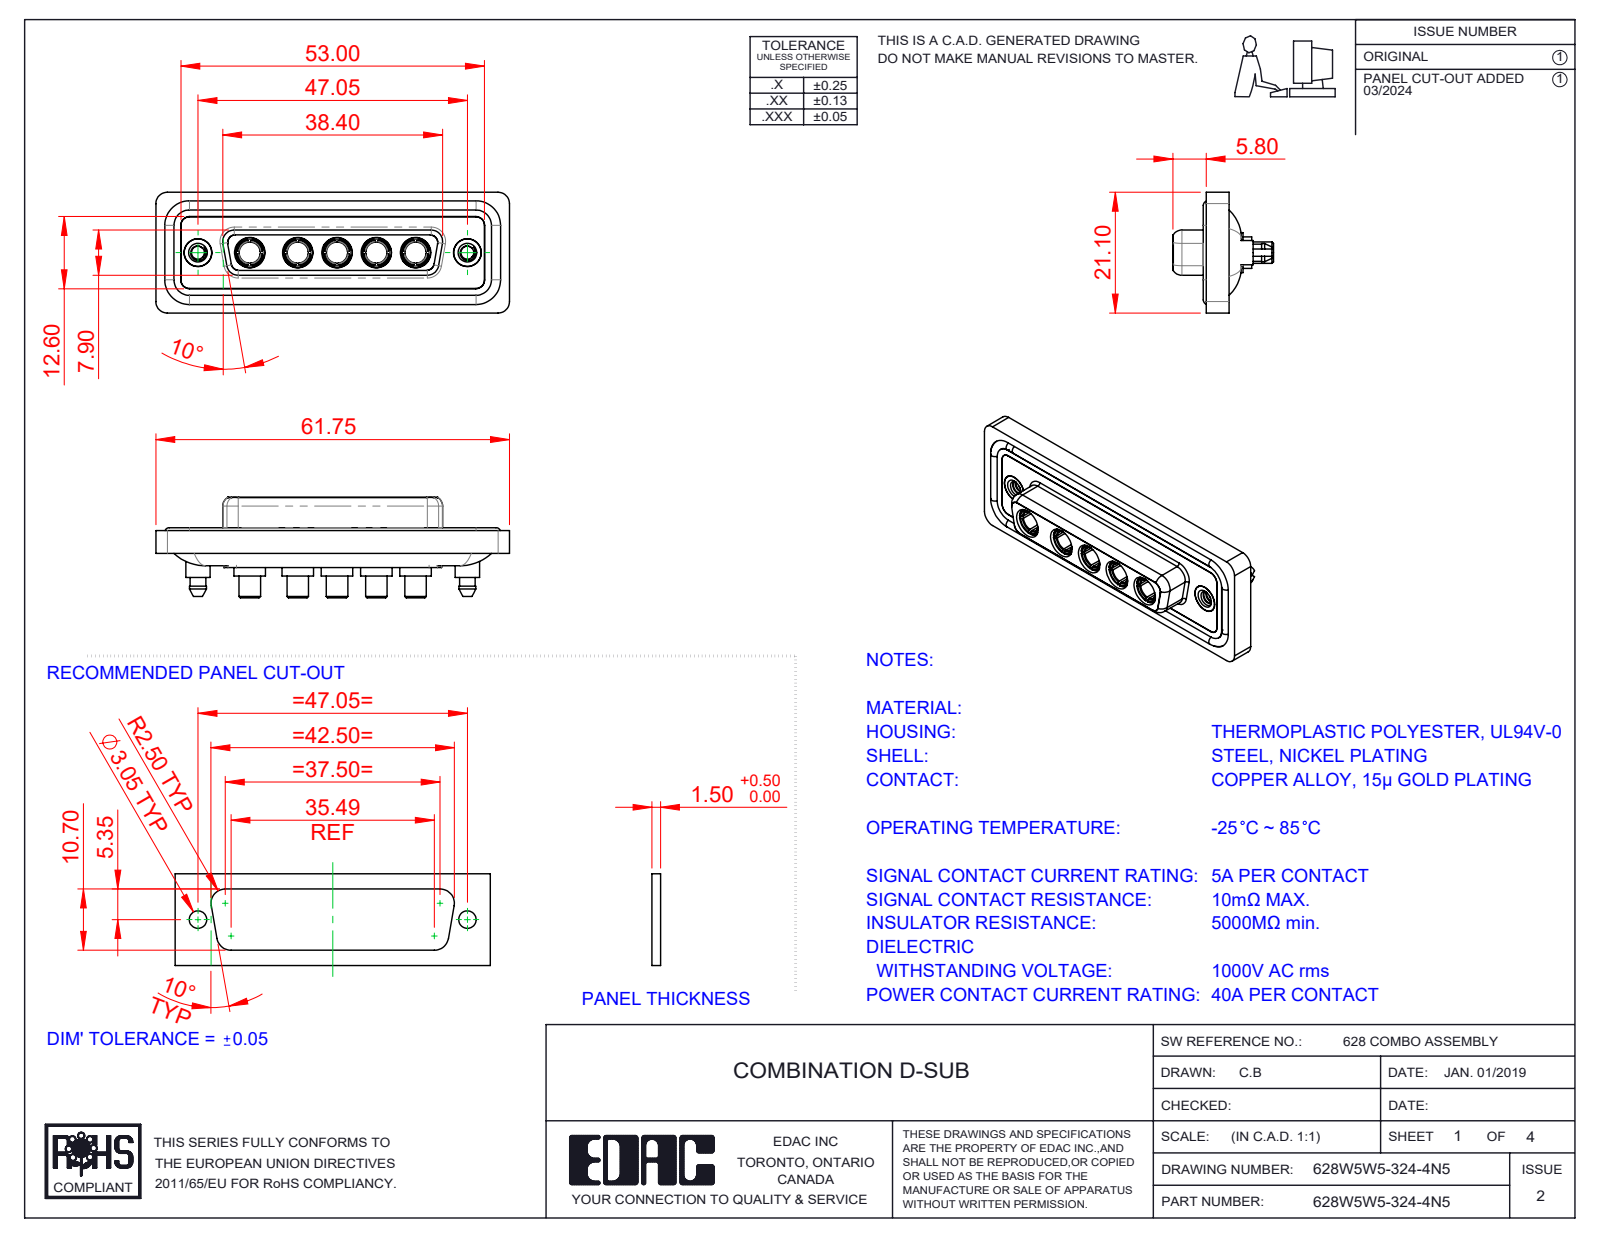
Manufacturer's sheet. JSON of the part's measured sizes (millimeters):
{"part_name": "628W5W5-324-4N5; 628Combo Threaded Boardlock_5; 628Combo Waterproof Housing_25 Contacts; 628Combo Shell Front_25 Contacts (+3 more)", "step_written_by": "SolidWorks 2023 (CONFIG_CONTROL_DESIGN)", "units": "millimeters", "bodies": {"solids": 17, "faces": 806, "planar": 266, "cylindrical": 335, "other": 205}, "overall_size": [61.75, 21.1, 17.55], "volume_mm3": 8399, "surface_area_mm2": 13803, "round_holes": [[4.85, 7], [3.7, 5], [5.3, 5], [2.26, 2], [4, 2], [4.05, 2], [5, 2]], "round_bosses_or_shafts": [[5.5, 5], [5.2, 5], [4.96, 5], [4.75, 5], [3.75, 5], [1.6, 4], [5.4, 2], [4.95, 2]], "partial_cylinders_radius": [[1.5, 24], [2, 18], [1.6, 10], [1.35, 8], [2.1, 5], [0.25, 4], [0.5, 4], [0.6, 4]], "face_to_face_distances": [0.4, 1.8, 7.45, 5.65, 0.5, 7.05, 6.6, 1.6, 1.1, 2.9], "hole_center_spacings": [6.86, 9.04, 13.72, 38.01, 8.39, 15.25, 15.9, 17.43]}
